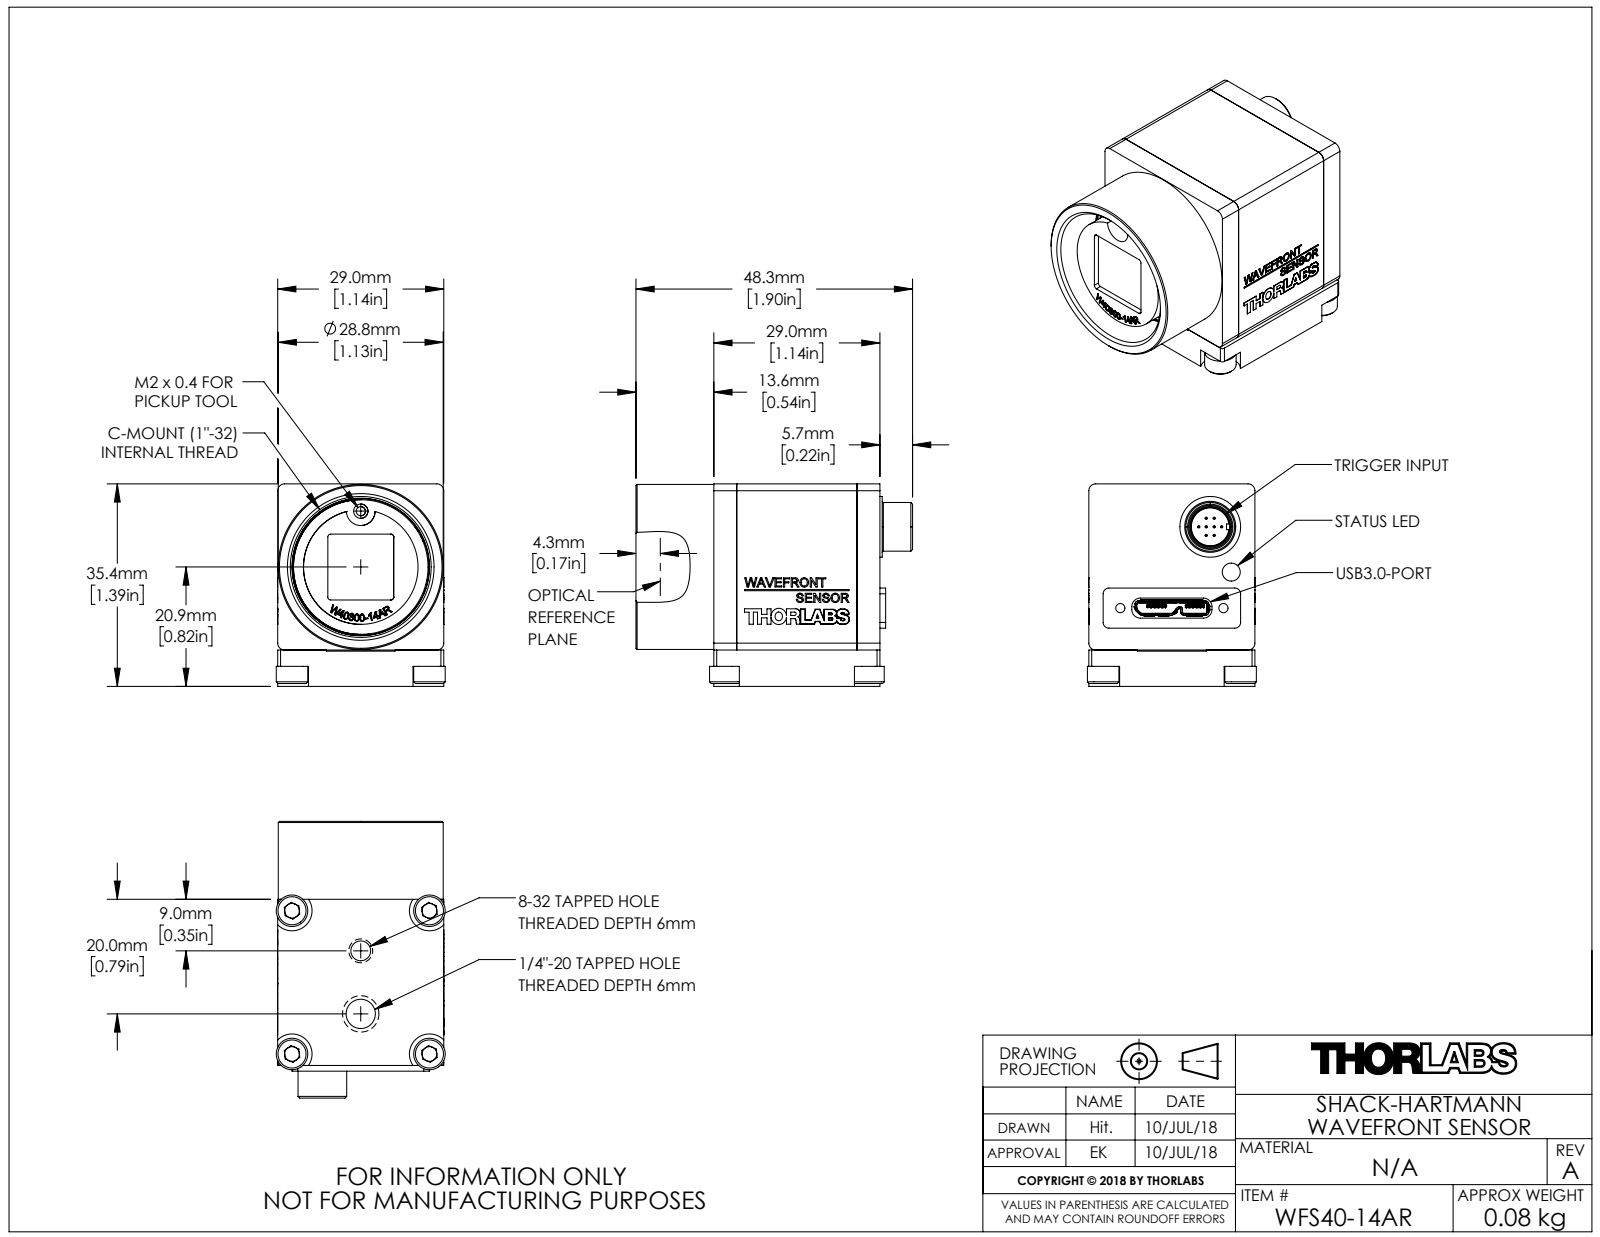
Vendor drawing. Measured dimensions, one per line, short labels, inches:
name: 20.05.05_MTN008533 WFS40-14AR
written by: SolidWorks 2018 (AUTOMOTIVE_DESIGN)
unit: in
bodies: 24 solids, 1976 faces (1517 planar, 206 cylindrical, 253 other)
size: 1.902 × 1.392 × 1.161
volume: 1.175 in³; area: 33.09 in²
holes: 11× ⌀0.126, 5× ⌀0.098, 3× ⌀0.063, 3× ⌀0.075, 1× ⌀0.039, 1× ⌀0.059, 1× ⌀0.13, 1× ⌀0.197, 1× ⌀0.268, 1× ⌀0.315, 1× ⌀0.945, 1× ⌀0.969
bosses: 11× ⌀0.118, 8× ⌀0.016, 4× ⌀0.217, 1× ⌀1.134, 1× ⌀0.925, 1× ⌀0.787, 1× ⌀0.417, 1× ⌀0.335
rounds: 19× R0.02, 12× R0.039, 10× R0.059, 8× R0.024, 8× R0.071, 7× R0.008, 7× R0.098, 6× R0.004
face distances: 0.024, 1.142, 1.118, 0.25, 0.656, 1.392, 0.189, 1.094, 0.844, 0.039
hole spacings: 0.384, 0.741, 0.383, 0.543, 0.665, 0.198, 0.199, 0.547
